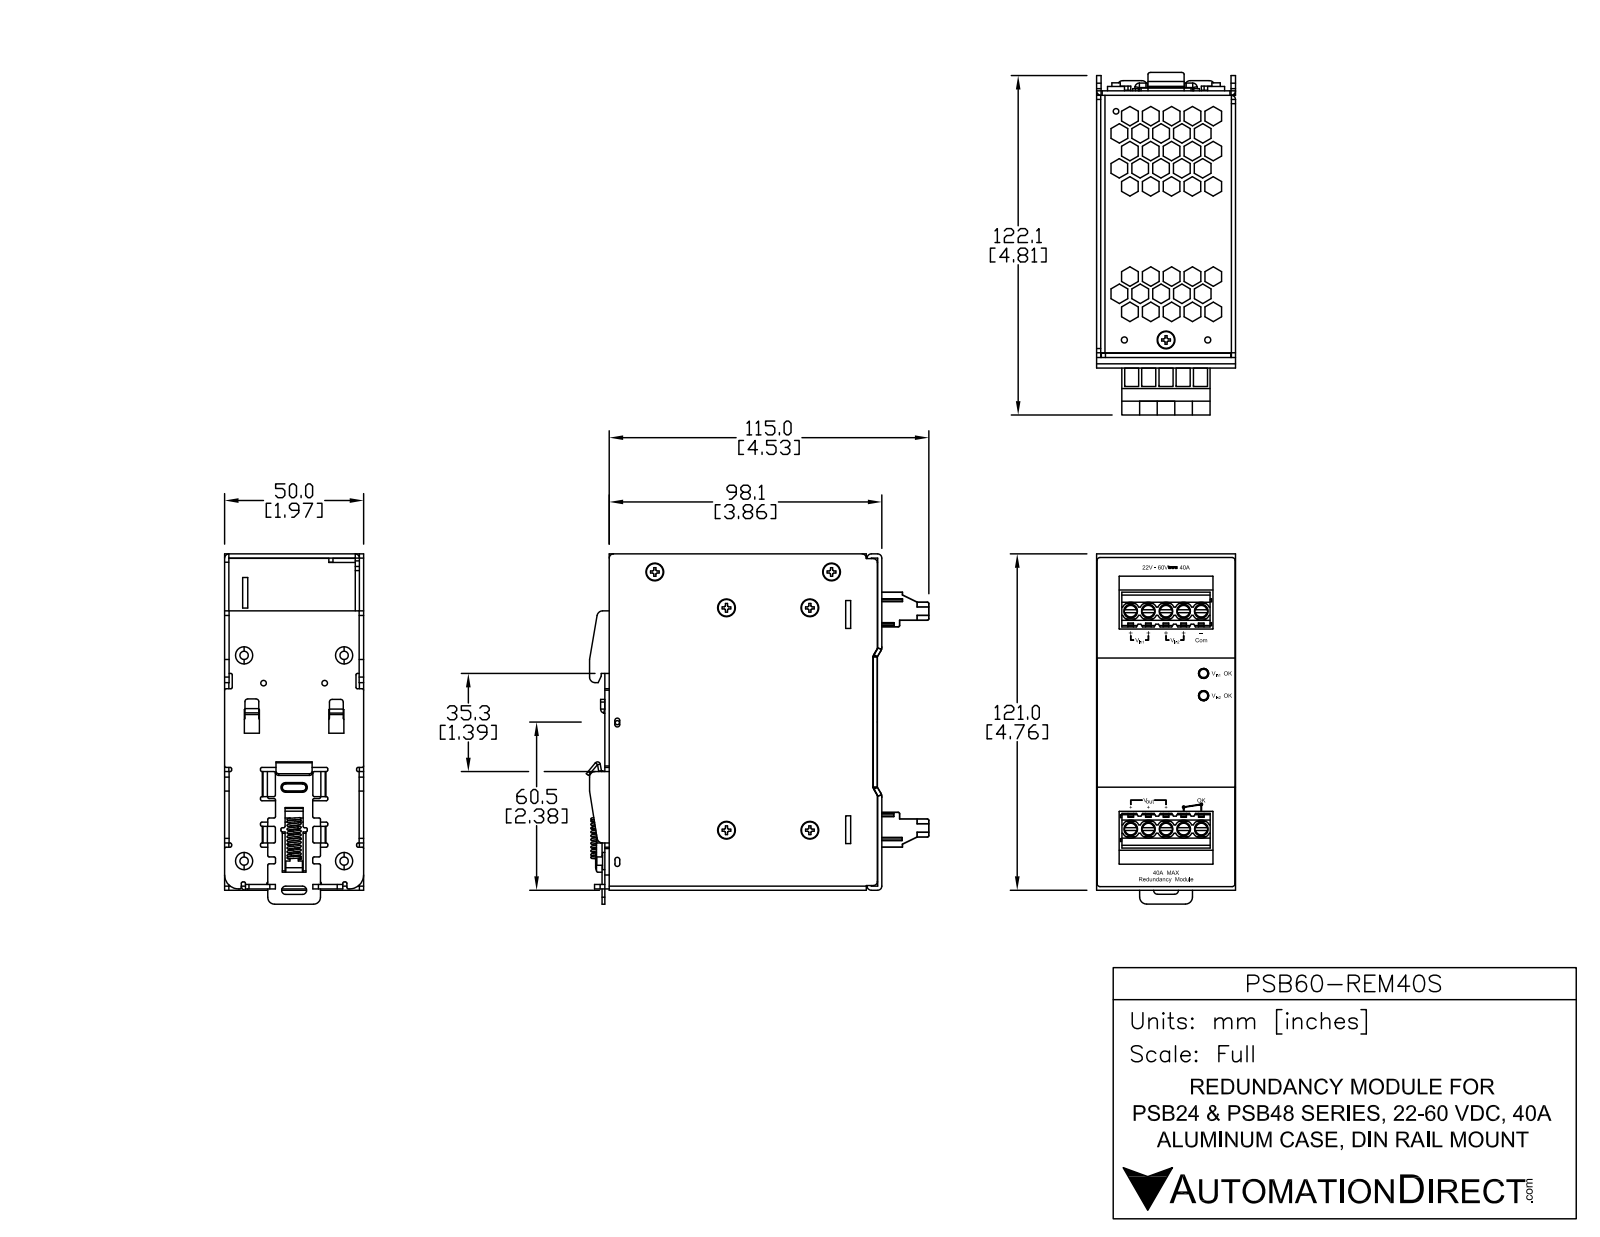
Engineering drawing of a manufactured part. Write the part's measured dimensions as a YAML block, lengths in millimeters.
part_name: "3100020600_2; 330307100101; 3105343000_1; 3460088100_2 (+8 more)"
step_written_by: "SolidWorks 2014 (AUTOMOTIVE_DESIGN)"
units: millimeters
bodies: {solids: 35, faces: 3664, planar: 2352, cylindrical: 701, other: 611}
overall_size: [126, 123.2, 54.4]
volume: 92820
surface_area: 135200
round_holes:
  - {diameter: 1.5, count: 10}
  - {diameter: 4, count: 10}
  - {diameter: 4.6, count: 10}
  - {diameter: 4.9, count: 10}
  - {diameter: 2.2, count: 6}
  - {diameter: 2.5, count: 4}
  - {diameter: 3, count: 4}
  - {diameter: 2, count: 3}
  - {diameter: 3.4, count: 2}
  - {diameter: 3.5, count: 2}
  - {diameter: 3.3, count: 1}
  - {diameter: 7.6, count: 1}
round_bosses_or_shafts:
  - {diameter: 4.7, count: 10}
  - {diameter: 6, count: 9}
  - {diameter: 3, count: 7}
  - {diameter: 5.2, count: 4}
  - {diameter: 2.7, count: 4}
  - {diameter: 7, count: 2}
  - {diameter: 8, count: 1}
  - {diameter: 7.6, count: 1}
partial_cylinders:
  - {radius: 0.5, count: 112}
  - {radius: 1.5, count: 36}
  - {radius: 1, count: 25}
  - {radius: 2, count: 18}
  - {radius: 0.1, count: 16}
  - {radius: 3.3, count: 10}
  - {radius: 1.6, count: 9}
  - {radius: 0.3, count: 6}
face_to_face_distances: [1.5, 48.5, 1.6, 50, 47, 91.9, 3.1, 96.5, 119.5, 93.5]
hole_center_spacings: [77.2, 6.4, 12.7, 1, 76.2, 77, 78, 77]
